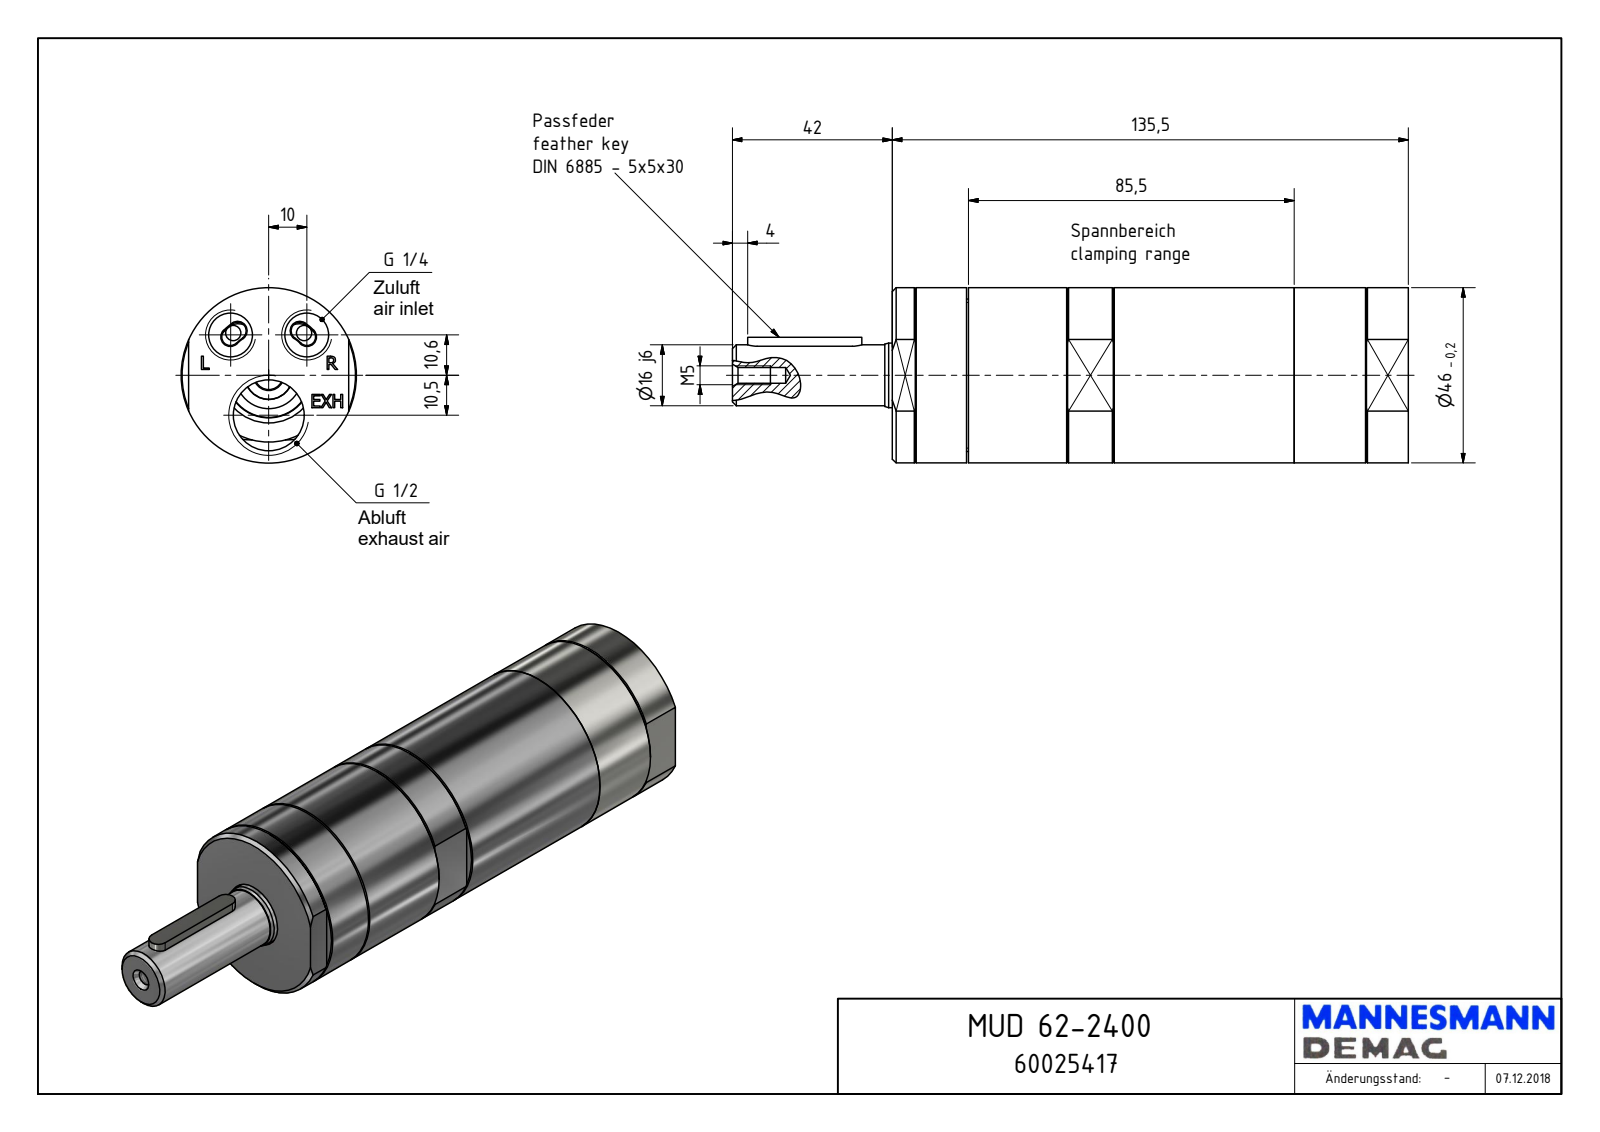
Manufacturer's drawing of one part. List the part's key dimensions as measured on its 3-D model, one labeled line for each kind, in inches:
Part name (STEP PRODUCT): MUD 62-2400_60025417
STEP written by: Autodesk Inventor 2018 (AUTOMOTIVE_DESIGN)
Units: inches
Bodies: 1 solid, 171 faces (98 planar, 37 cylindrical, 36 other)
Overall size (bounding box): 6.988 × 1.811 × 1.811
Volume: 13.86 in³ · Surface area: 46.04 in²
Round holes (diameter × count): ⌀0.451 ×2, ⌀0.163 ×1, ⌀0.689 ×1, ⌀0.733 ×1, ⌀0.846 ×1, ⌀0.906 ×1
Round bosses / shafts (diameter × count): ⌀1.811 ×1, ⌀1.575 ×1, ⌀1.307 ×1, ⌀0.77 ×1, ⌀0.667 ×1, ⌀0.63 ×1
Partial cylindrical surfaces — rounded edges, fillets, slot ends (radius × count): R0.098 ×6, R0.197 ×2, R0.659 ×1, R0.748 ×1
Main face-to-face distances: 5.335, 1.654, 0.787, 4.547, 0.768, 0.02, 4.567, 5.065, 4.297, 4.278
Hole centre spacings: 0.574, 0.919, 0.413, 0.787
